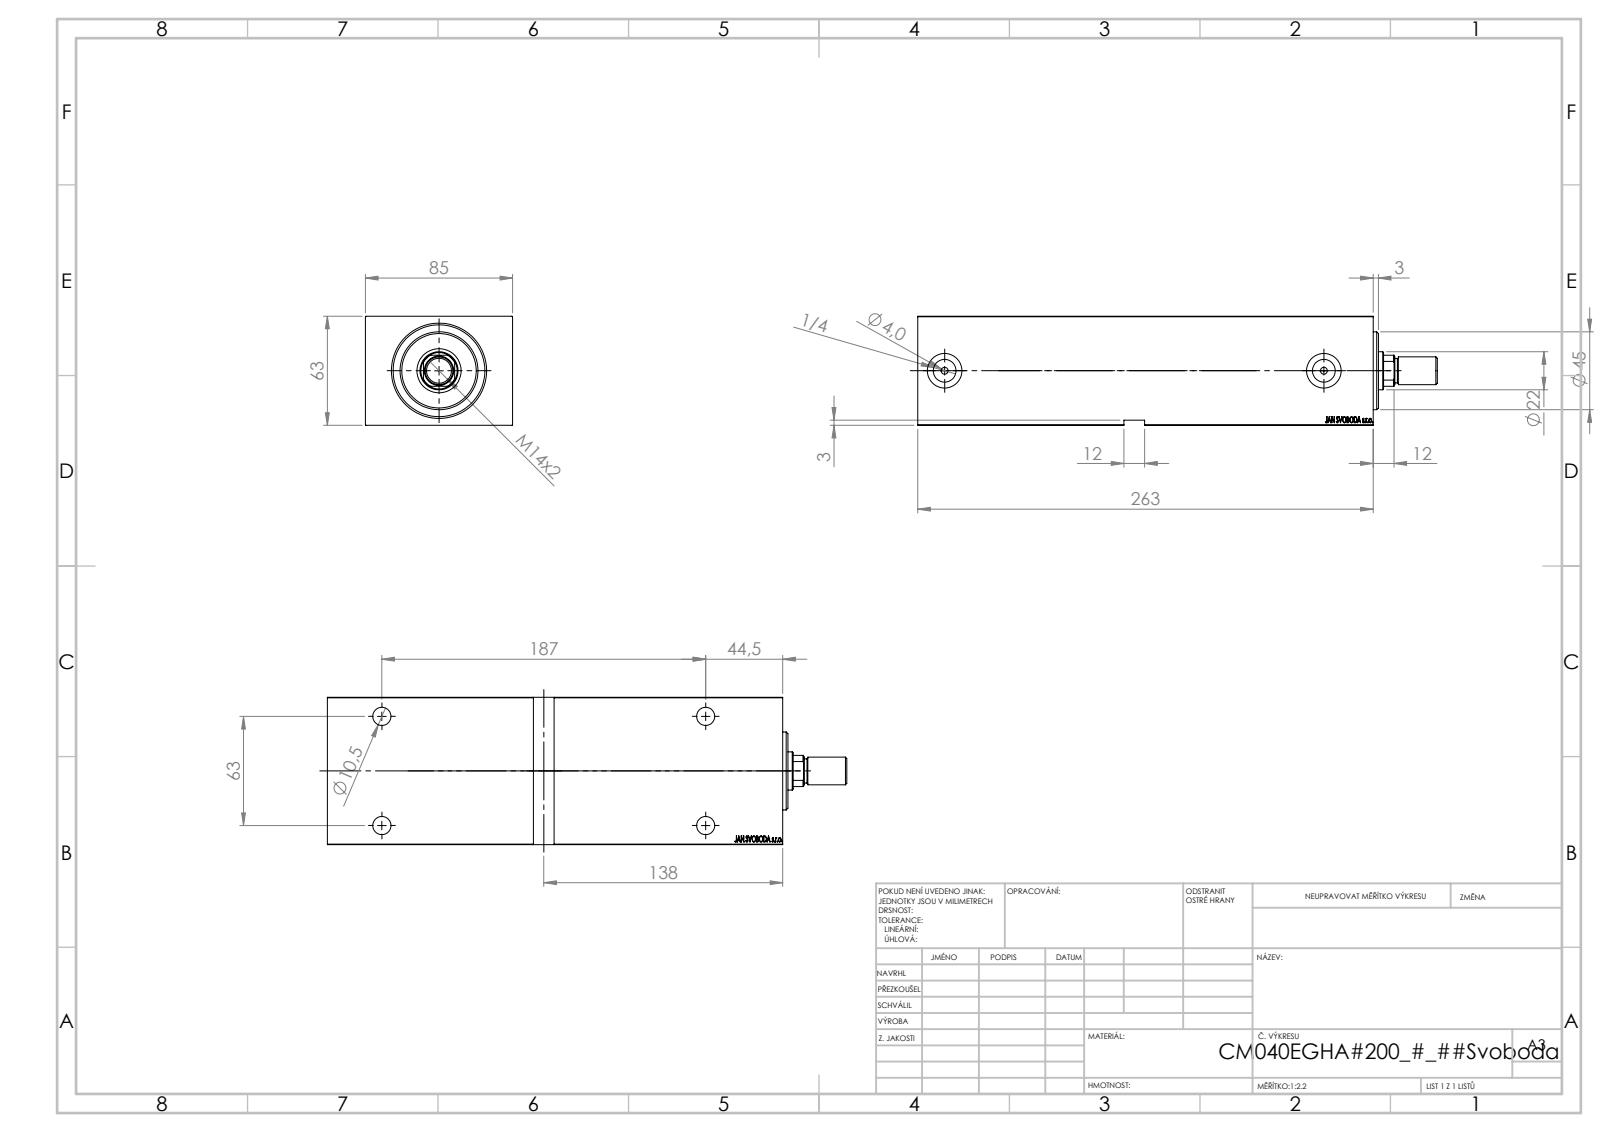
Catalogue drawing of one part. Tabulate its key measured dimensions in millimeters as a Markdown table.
| quantity | value |
| --- | --- |
| part name | V450CM_E_Body; V450CM_E_VCP; V450CM_MALE_METRIC; V450CM_VC_B |
| STEP written by | SolidWorks 2019 (CONFIG_CONTROL_DESIGN) |
| units | millimeters |
| bodies | 4 solids, 870 faces (414 planar, 56 cylindrical, 400 other) |
| overall size | 300 × 85 × 63 |
| volume | 1 211 000 mm³ |
| surface area | 163 864 mm² |
| round holes (diameter × count) | 10.5 × 4, 16.5 × 4, 4 × 2, 13.16 × 2, 20 × 2, 12.5 × 1, 22 × 1, 25.5 × 1, 40 × 1, 53 × 1 |
| round bosses / shafts (diameter × count) | 45 × 1, 42 × 1, 16 × 1, 14 × 1 |
| partial cylindrical surfaces (radius × count) | 10.5 × 1 |
| main face-to-face distances | 63, 85, 263, 12, 251, 3, 5, 258, 246, 60 |
| hole center spacings | 63, 187, 197.33, 219 |
